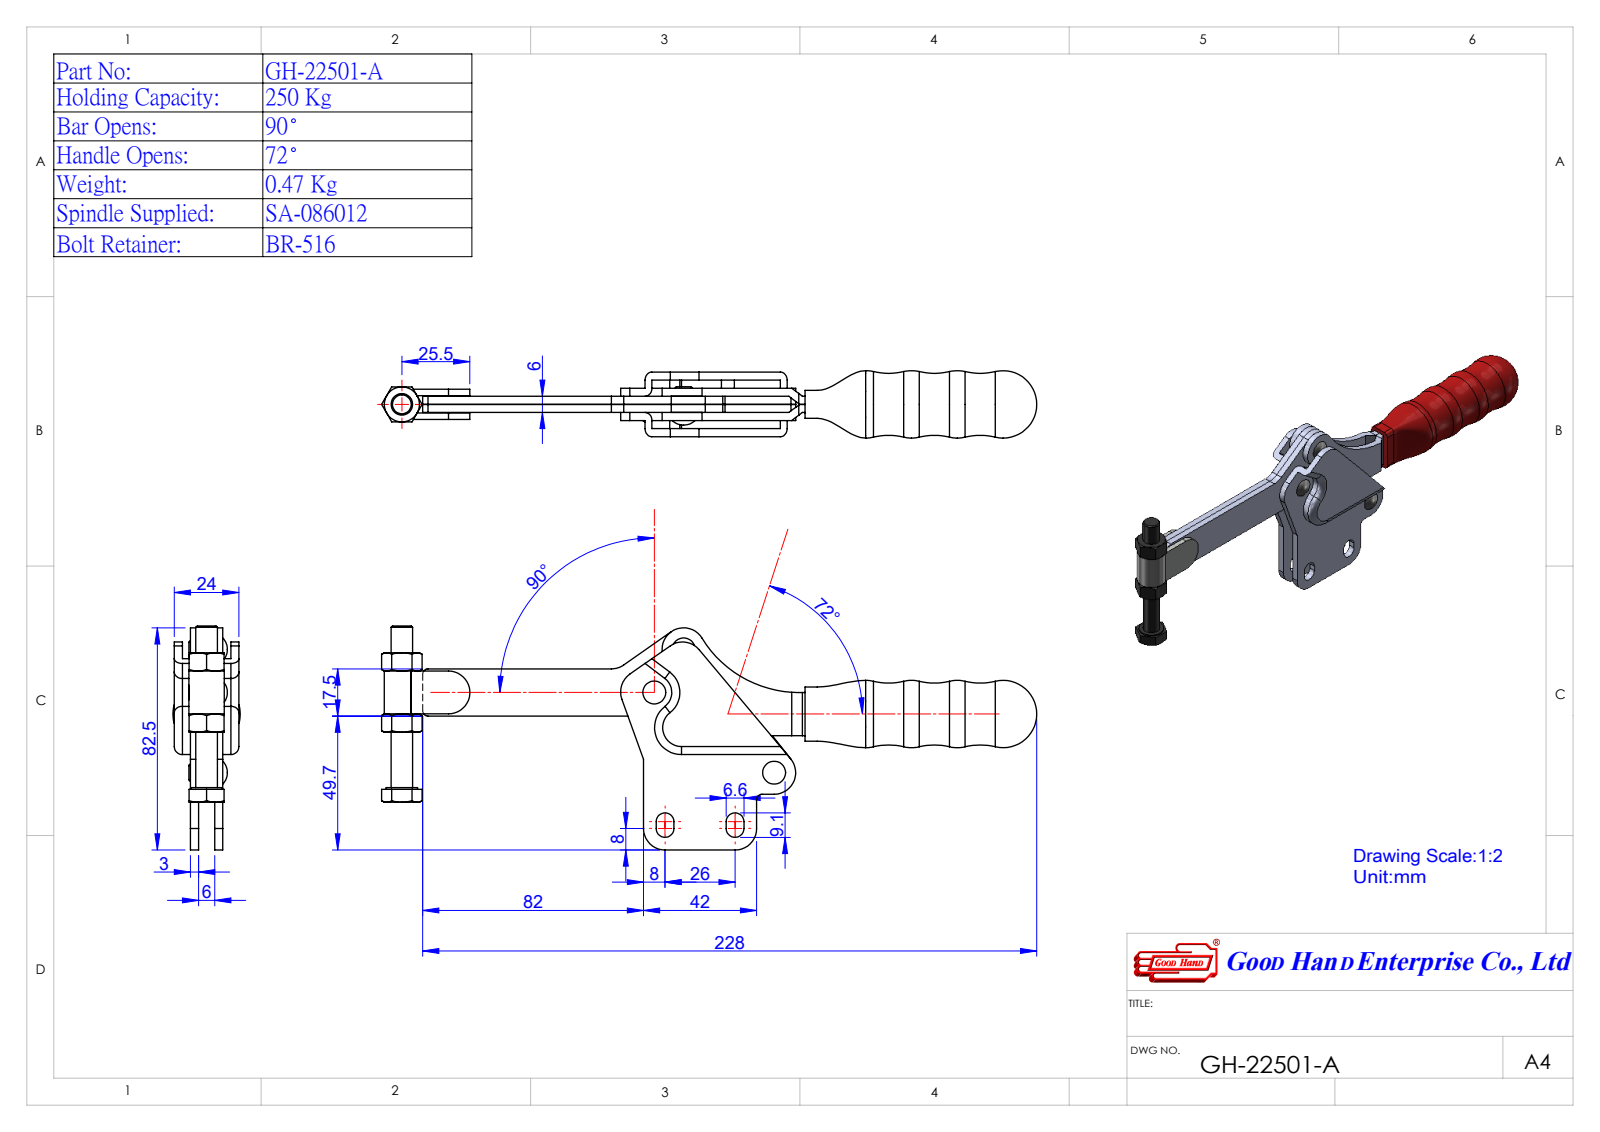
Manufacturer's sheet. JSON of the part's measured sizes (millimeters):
{"part_name": "Group1^GH-22501-A(簡化)-1; Group1^GH-22501-A(簡化); Group4^GH-22501-A(簡化)-1; GH-22501-A(簡化)-1 (+2 more)", "step_written_by": "SolidWorks 2016 (AUTOMOTIVE_DESIGN)", "units": "millimeters", "bodies": {"solids": 5, "faces": 315, "planar": 122, "cylindrical": 123, "other": 70}, "overall_size": [239.63, 83.15, 25], "volume_mm3": 85588, "surface_area_mm2": 41097, "round_holes": [[5, 4], [6.35, 2], [6.3, 1]], "round_bosses_or_shafts": [[4.8, 4], [11.63, 1], [8, 1]], "partial_cylinders_radius": [[8, 8], [3.3, 4], [1, 3], [2, 3], [2.42, 2], [4.15, 1], [6.5, 1], [6.55, 1]], "face_to_face_distances": [6, 3, 9, 12, 15, 18, 21, 8.8, 24, 6.4], "hole_center_spacings": [20.06, 36.71, 0.37, 9.09, 9.14, 19.36, 22.7, 23]}
